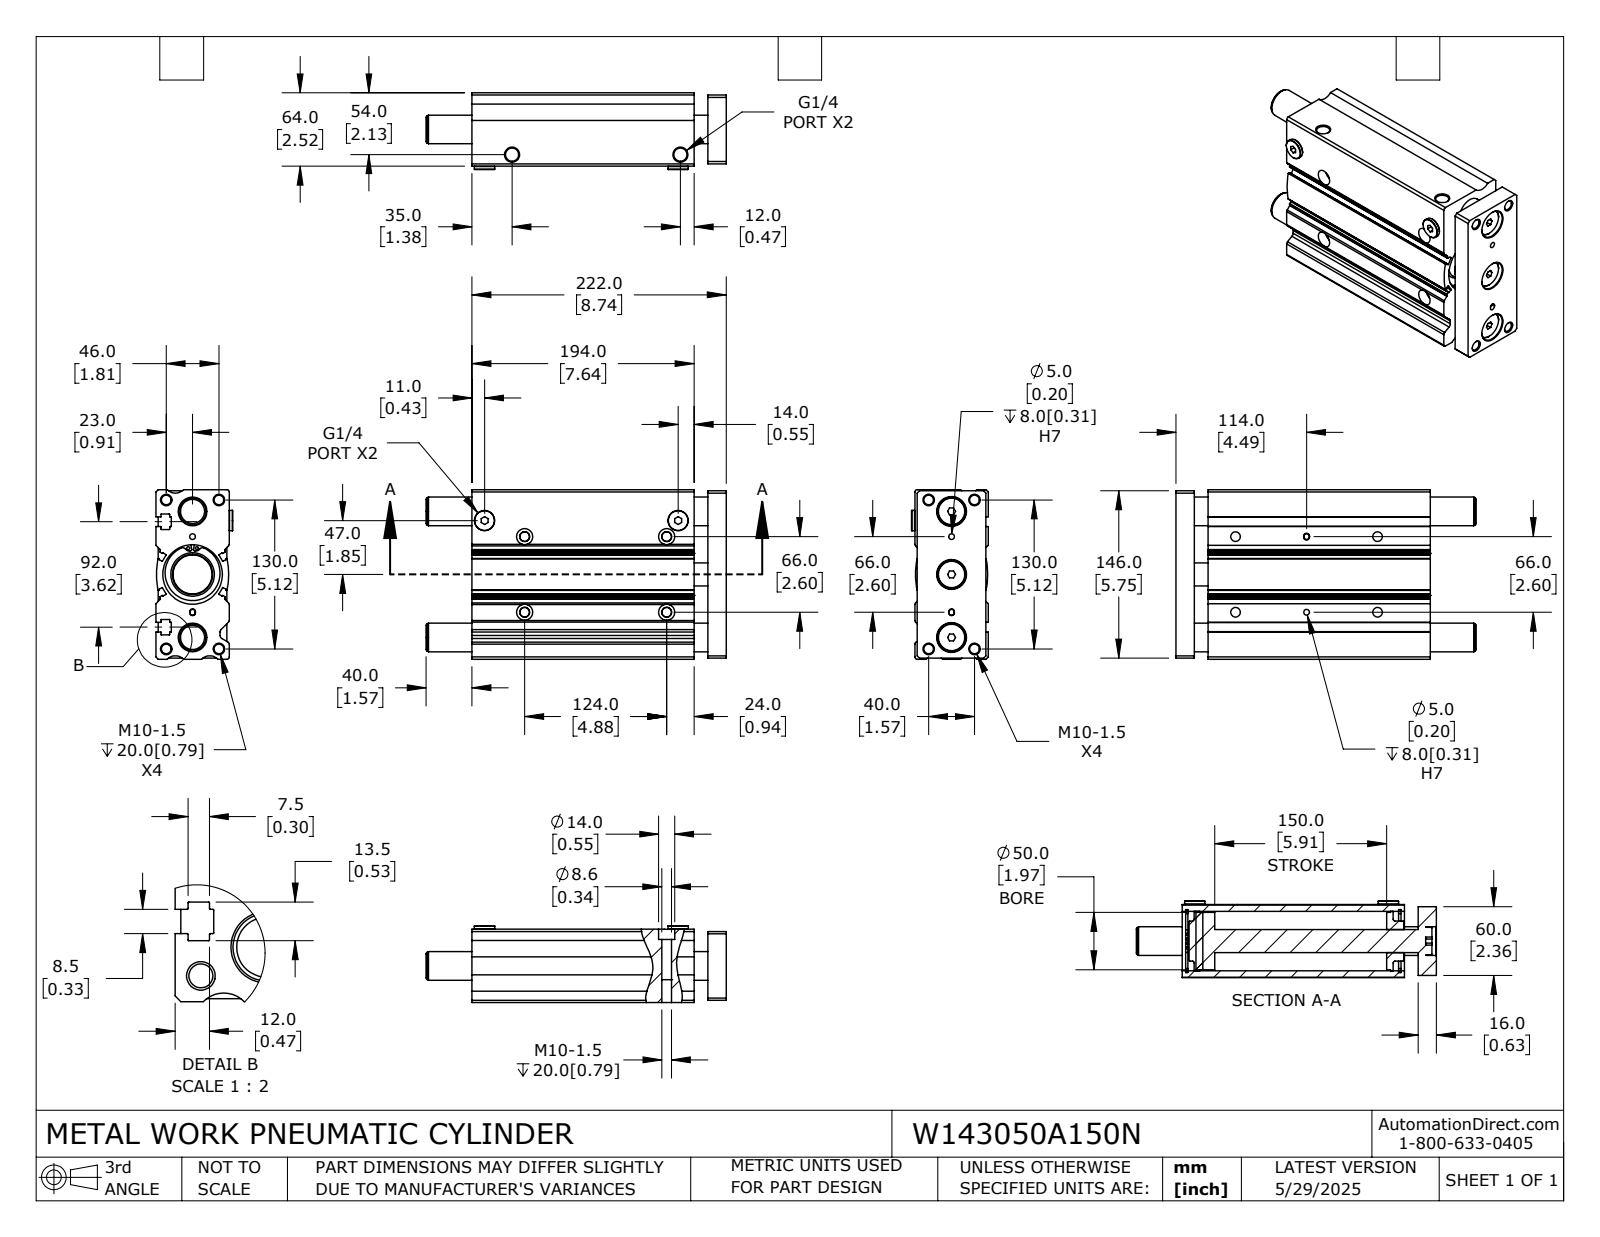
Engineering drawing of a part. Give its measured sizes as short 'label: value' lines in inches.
name: W143050A150N; W143050A150N_ROD; W143050A150N_BODY
written by: SolidWorks 2024 (CONFIG_CONTROL_DESIGN)
unit: in
bodies: 6 solids, 466 faces (186 planar, 224 cylindrical, 56 other)
size: 10.315 × 5.827 × 2.638
volume: 94.64 in³; area: 454.8 in²
holes: 12× ⌀0.33, 4× ⌀0.098, 4× ⌀0.197, 4× ⌀0.339, 4× ⌀0.551, 3× ⌀0.984, 2× ⌀0.451, 2× ⌀1.89, 1× ⌀0.787
bosses: 3× ⌀0.945, 2× ⌀0.697, 1× ⌀2.165, 1× ⌀2.047, 1× ⌀1.969, 1× ⌀1.378
rounds: 44× R0.012, 12× R0.02, 10× R0.118, 6× R0.079, 6× R2.677, 4× R0.039, 4× R0.098, 3× R0.394
face distances: 2.52, 0.472, 7.638, 0.63, 8.11, 5.827, 0.098, 0.079, 0.531, 1.102
hole spacings: 0.118, 0.424, 0.869, 0.88, 0.916, 0.963, 0.987, 1.271
